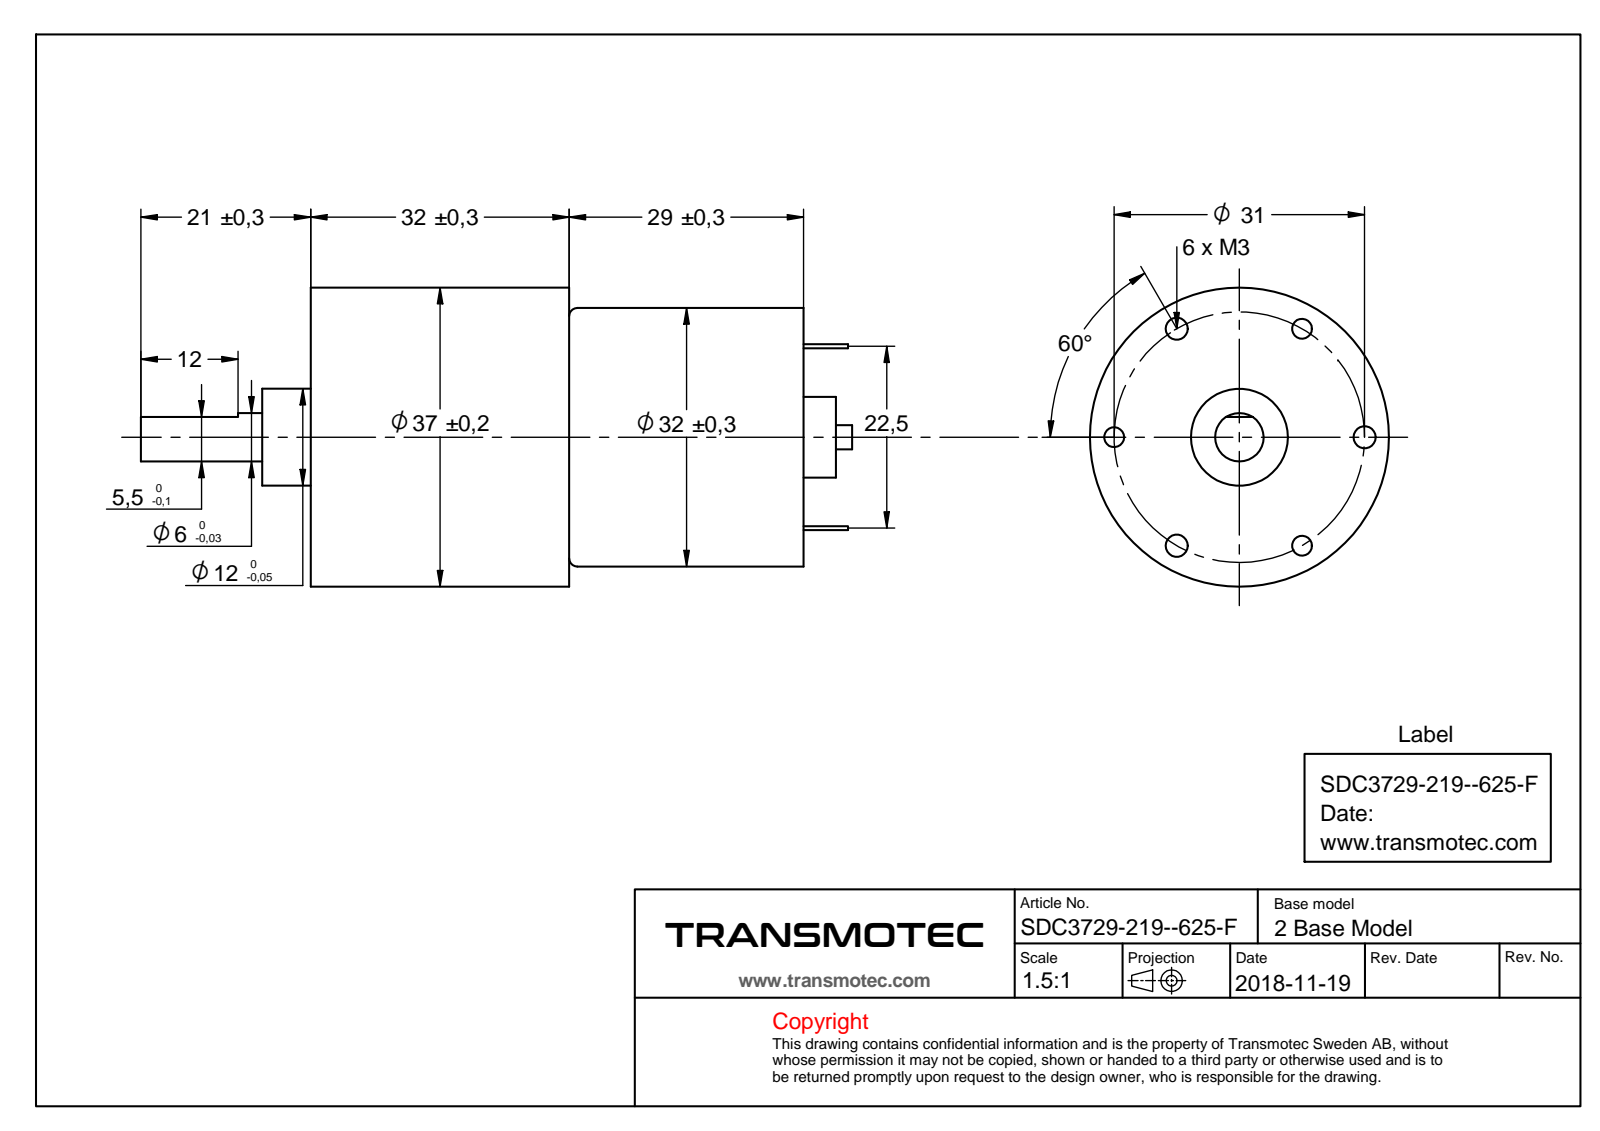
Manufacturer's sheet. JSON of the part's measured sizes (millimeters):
{"step_written_by": "Unknown (AUTOMOTIVE_DESIGN)", "units": "millimeters", "bodies": {"solids": 1, "faces": 38, "planar": 25, "cylindrical": 12, "other": 1}, "overall_size": [88, 37, 37], "volume_mm3": 58983, "surface_area_mm2": 9910, "round_holes": [[2.46, 3], [2.74, 3]], "round_bosses_or_shafts": [[37, 1], [32, 1], [12, 1], [10, 1], [6, 1], [3, 1]], "face_to_face_distances": [61, 32, 29, 6, 67, 38, 71, 65, 33, 4], "hole_center_spacings": [15.5, 26.85, 26.84, 30.99, 31]}
